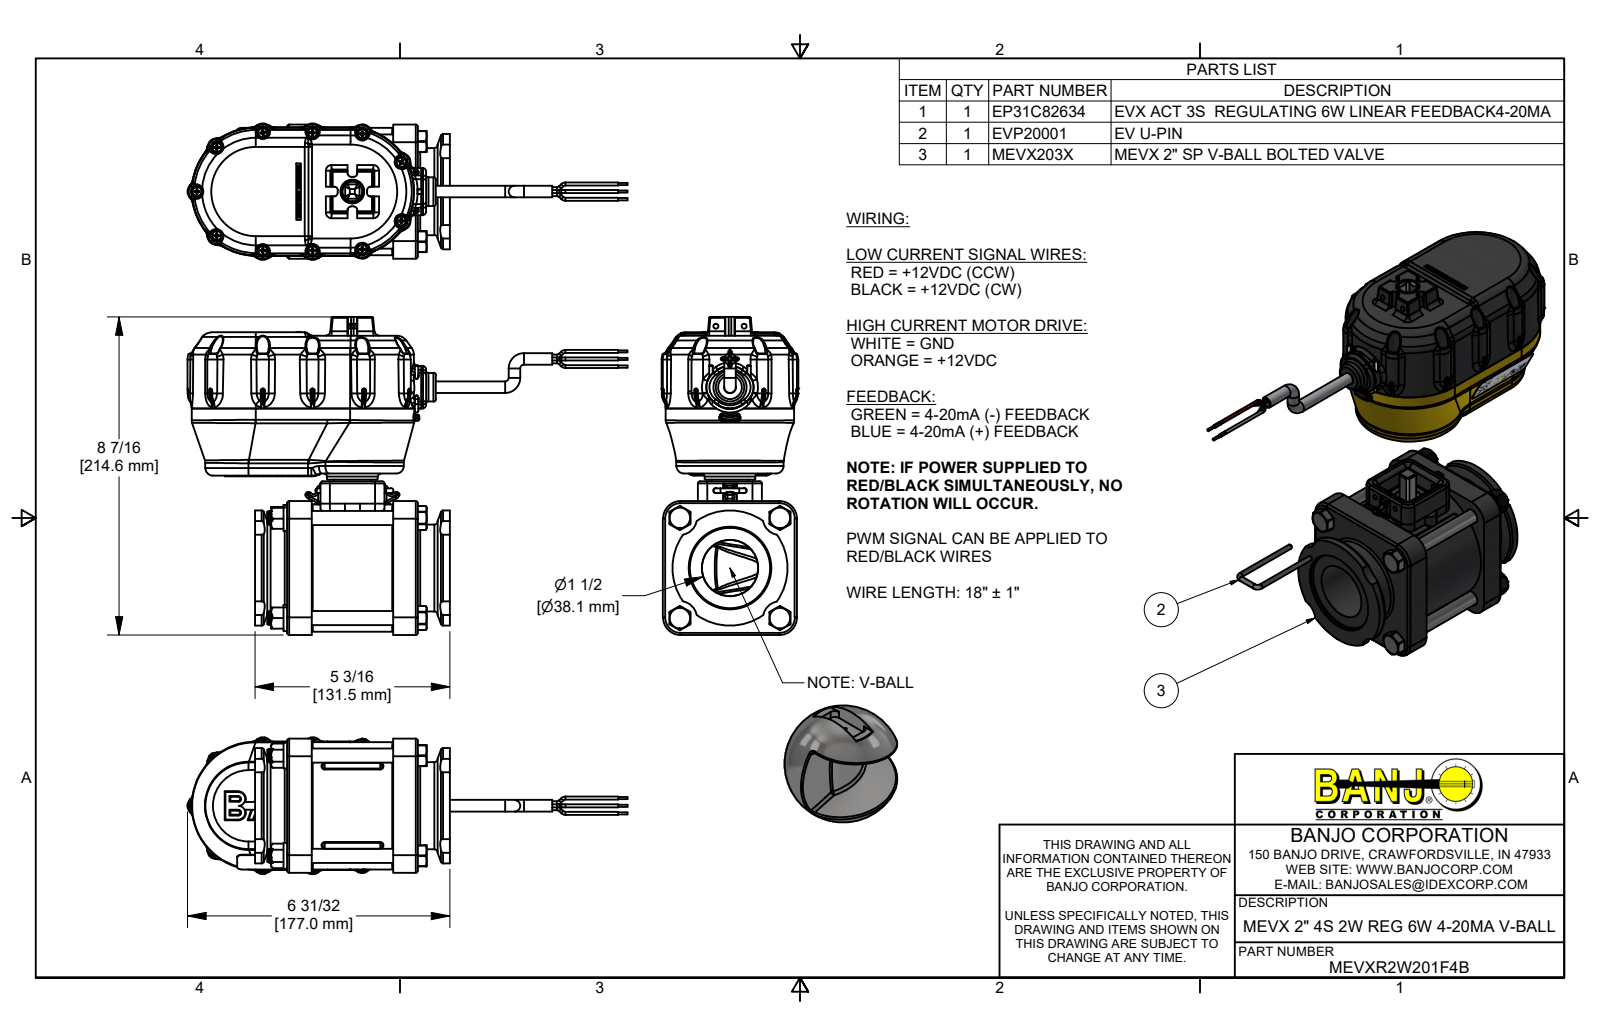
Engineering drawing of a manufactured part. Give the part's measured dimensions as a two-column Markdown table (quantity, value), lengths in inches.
| quantity | value |
| --- | --- |
| part name | MEVXR2W201F4B; EP31C82634; B61905PPHS; EP20KIT (+8 more) |
| STEP written by | Autodesk Inventor 2022 (AUTOMOTIVE_DESIGN) |
| units | inches |
| bodies | 626 solids, 18455 faces (6992 planar, 6243 cylindrical, 5220 other) |
| overall size | 11.685 × 8.448 × 3.63 |
| volume | 68.69 in³ |
| surface area | 683.6 in² |
| round holes (diameter × count) | 0.01 × 184, 0.009 × 27, 0.012 × 27, 0.029 × 12, 0.019 × 11, 0.095 × 11, 0.15 × 11, 0.076 × 10, 0.033 × 7, 0.017 × 6, 0.067 × 6, 0.097 × 4 |
| round bosses / shafts (diameter × count) | 0.026 × 167, 0.324 × 60, 0.028 × 27, 0.08 × 20, 0.25 × 17, 0.14 × 11, 0.108 × 11, 0.085 × 11 |
| partial cylindrical surfaces (radius × count) | 0.04 × 152, 0.02 × 97, 0.01 × 76, 0.005 × 74, 0.004 × 52, 0.015 × 44, 0.06 × 36, 0.03 × 31 |
| main face-to-face distances | 0.078, 0.1, 0.076, 2.565, 1.685, 0.175, 1.983, 1.417, 0.08, 0.537 |
| hole center spacings | 1.283, 1.88, 2.659, 2.73, 2.967, 3.45, 0.487, 0.492 |
